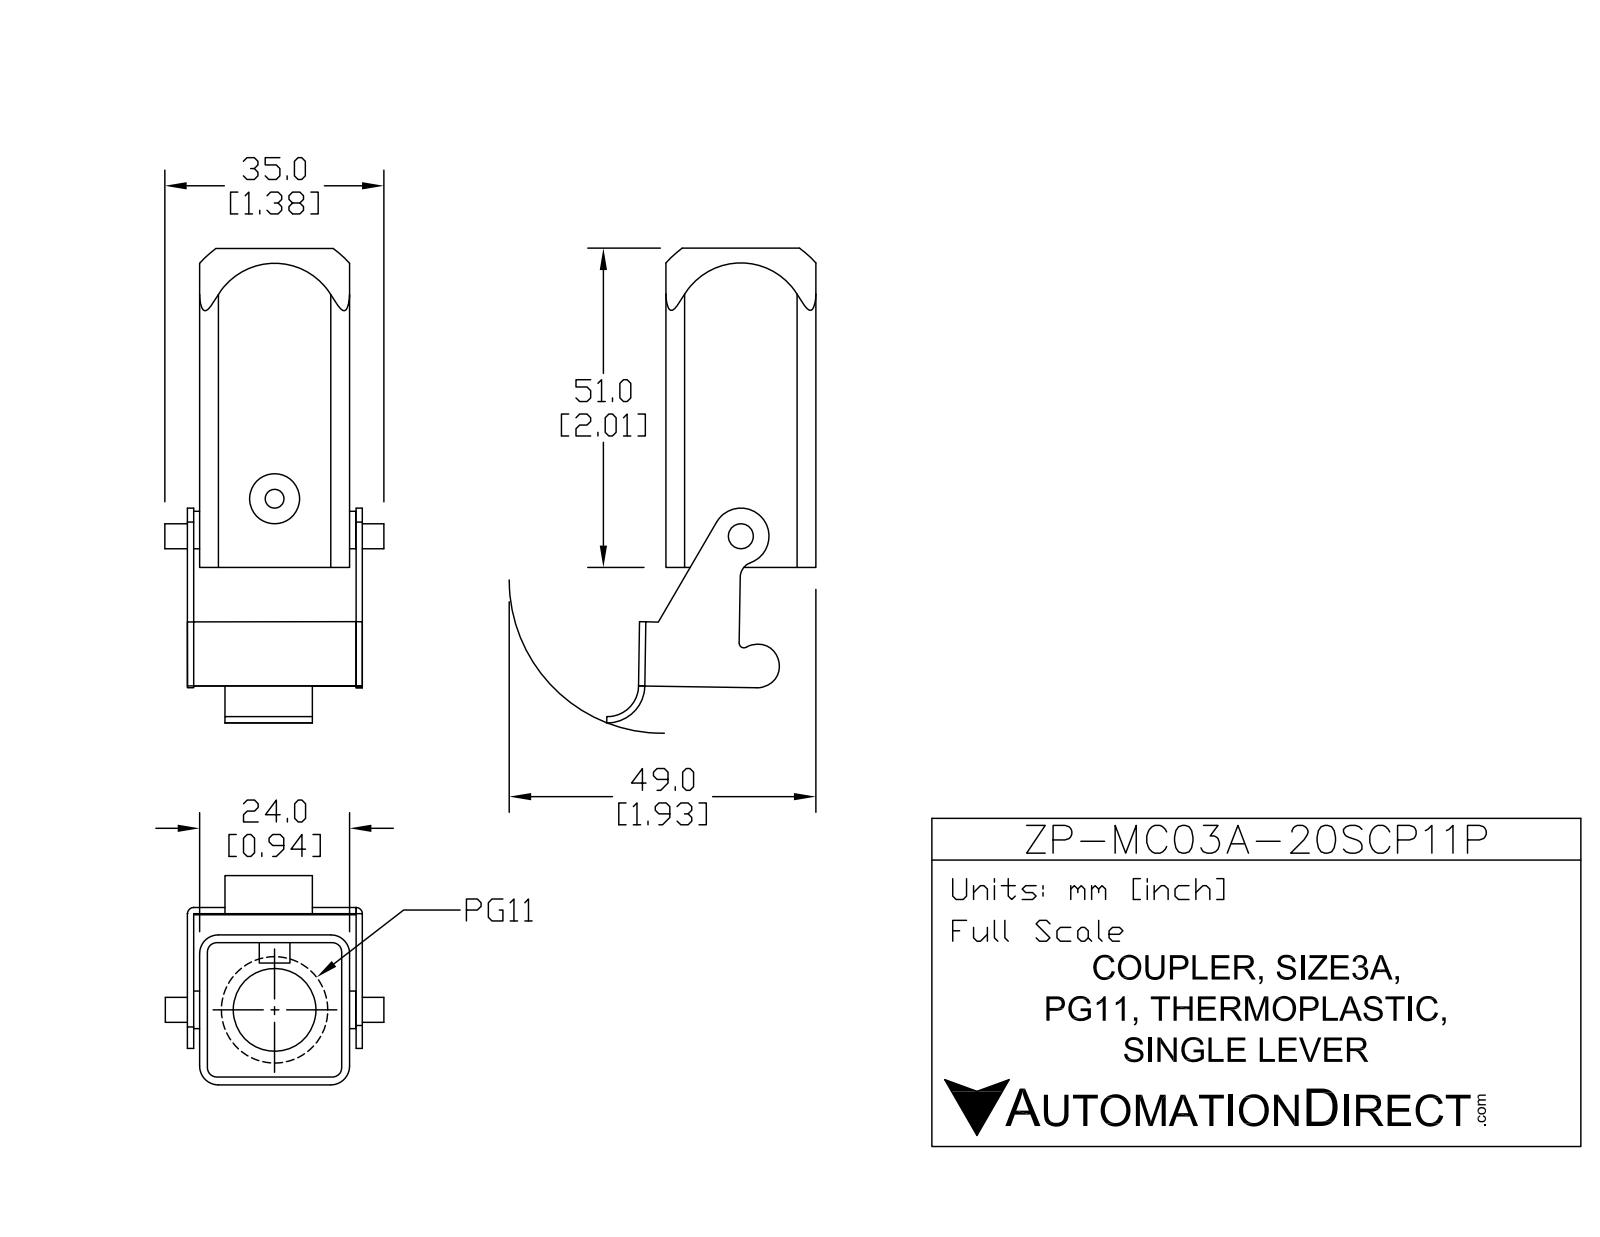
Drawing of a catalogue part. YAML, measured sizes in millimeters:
part_name: "ZP-MC03A-2-SCP11P"
step_written_by: "SolidWorks 2011 (AUTOMOTIVE_DESIGN)"
units: millimeters
bodies: {solids: 2, faces: 97, planar: 46, cylindrical: 45, other: 6}
overall_size: [50.54, 41.96, 35]
volume: 9130
surface_area: 11485
round_holes:
  - {diameter: 3, count: 1}
  - {diameter: 4.5, count: 1}
  - {diameter: 13.25, count: 1}
  - {diameter: 17, count: 1}
round_bosses_or_shafts:
  - {diameter: 6, count: 1}
  - {diameter: 4, count: 1}
partial_cylinders:
  - {radius: 1, count: 10}
  - {radius: 0.5, count: 6}
  - {radius: 3, count: 6}
  - {radius: 1.5, count: 4}
  - {radius: 1.4, count: 1}
  - {radius: 1.74, count: 1}
  - {radius: 3.15, count: 1}
  - {radius: 4.69, count: 1}
face_to_face_distances: [1.25, 22.75, 24, 21.5, 1, 3.25, 2, 27, 3, 26]
